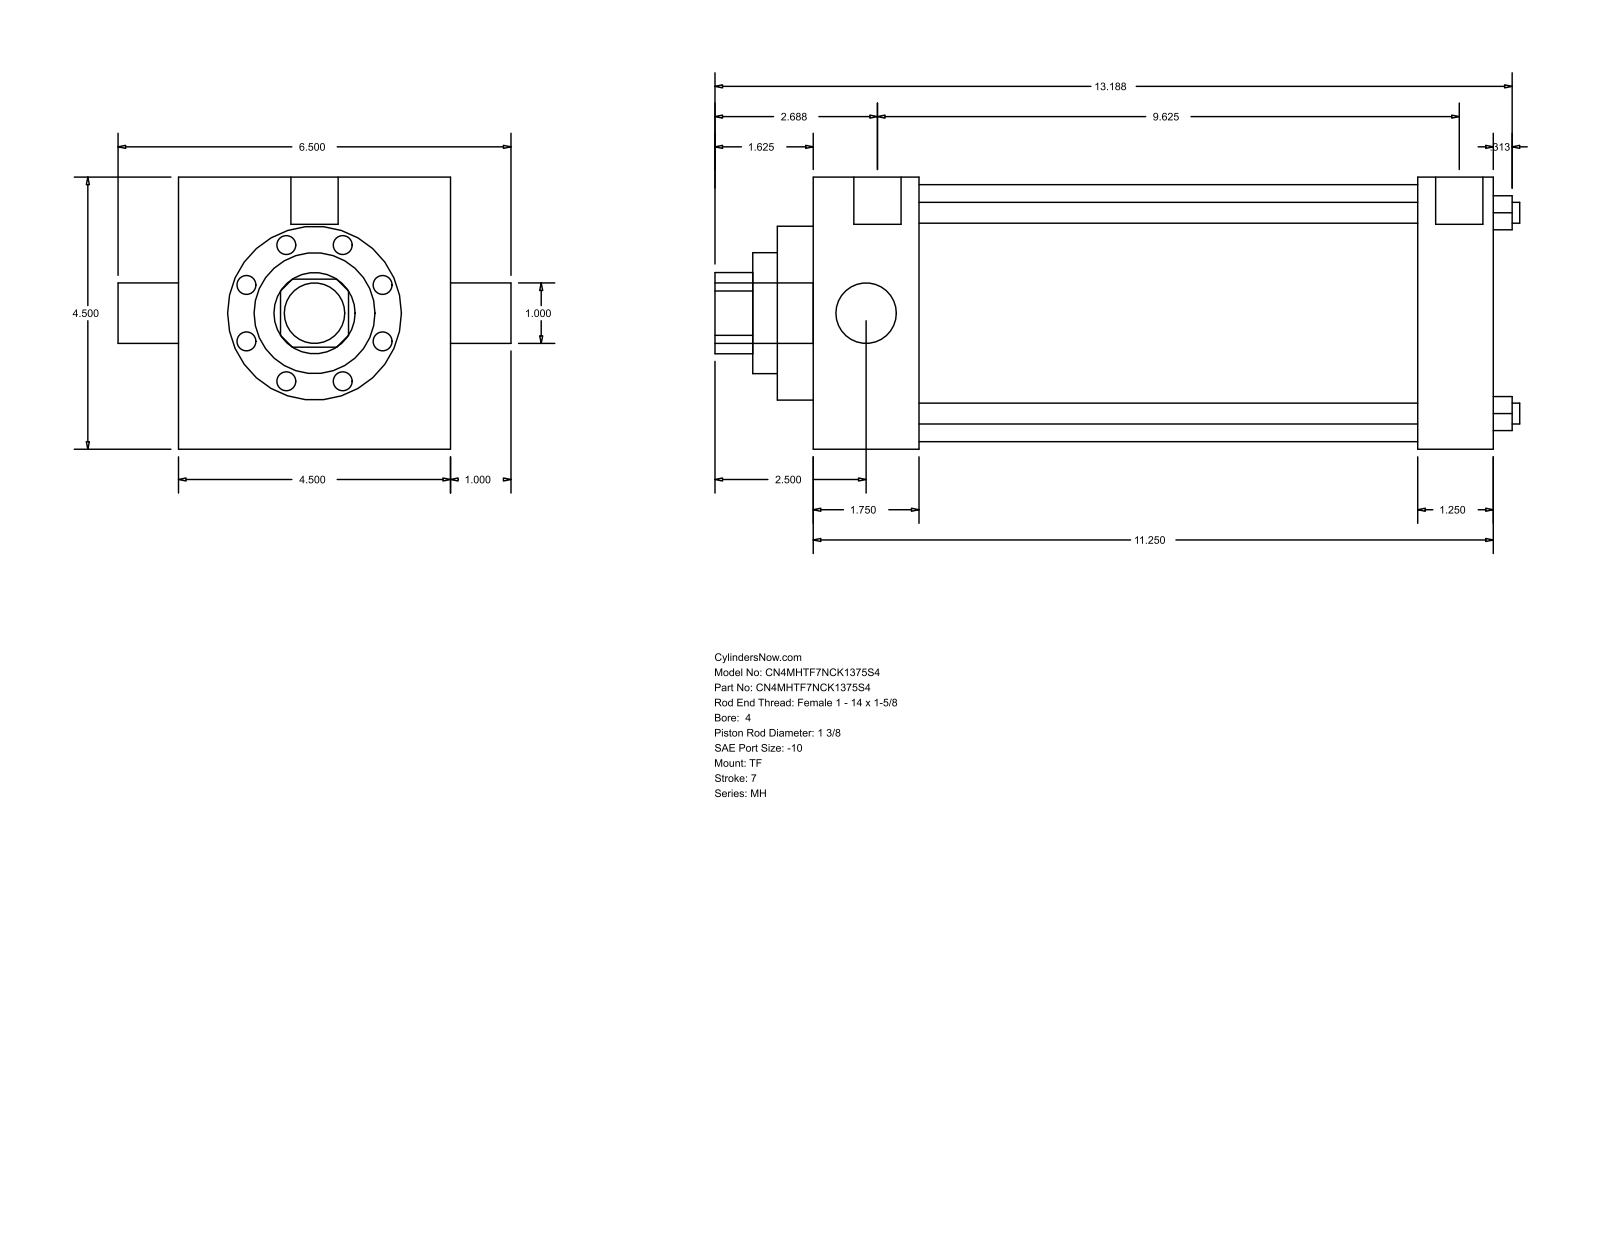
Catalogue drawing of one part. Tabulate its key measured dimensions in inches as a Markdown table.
| quantity | value |
| --- | --- |
| part name | MH_TF__0400_1.375 |
| STEP written by | GSSL Pune (CONFIG_CONTROL_DESIGN) |
| units | inches |
| bodies | 0 solids, 86 faces (61 planar, 25 cylindrical, 0 other) |
| overall size | 13.313 × 6.5 × 4.5 |
| round holes (diameter × count) | 0.345 × 4, 1 × 1, 1.375 × 1, 2 × 1, 2.875 × 1, 4.25 × 1 |
| round bosses / shafts (diameter × count) | 0.344 × 3, 0.781 × 2, 1 × 1 |
| partial cylindrical surfaces (radius × count) | 0.672 × 1 |
| main face-to-face distances | 4.5, 11.25, 1.75, 9.5, 10, 8.25, 1.25, 0.594, 2.344, 10.594 |
| hole center spacings | 2.347, 3.32, 4.695 |
